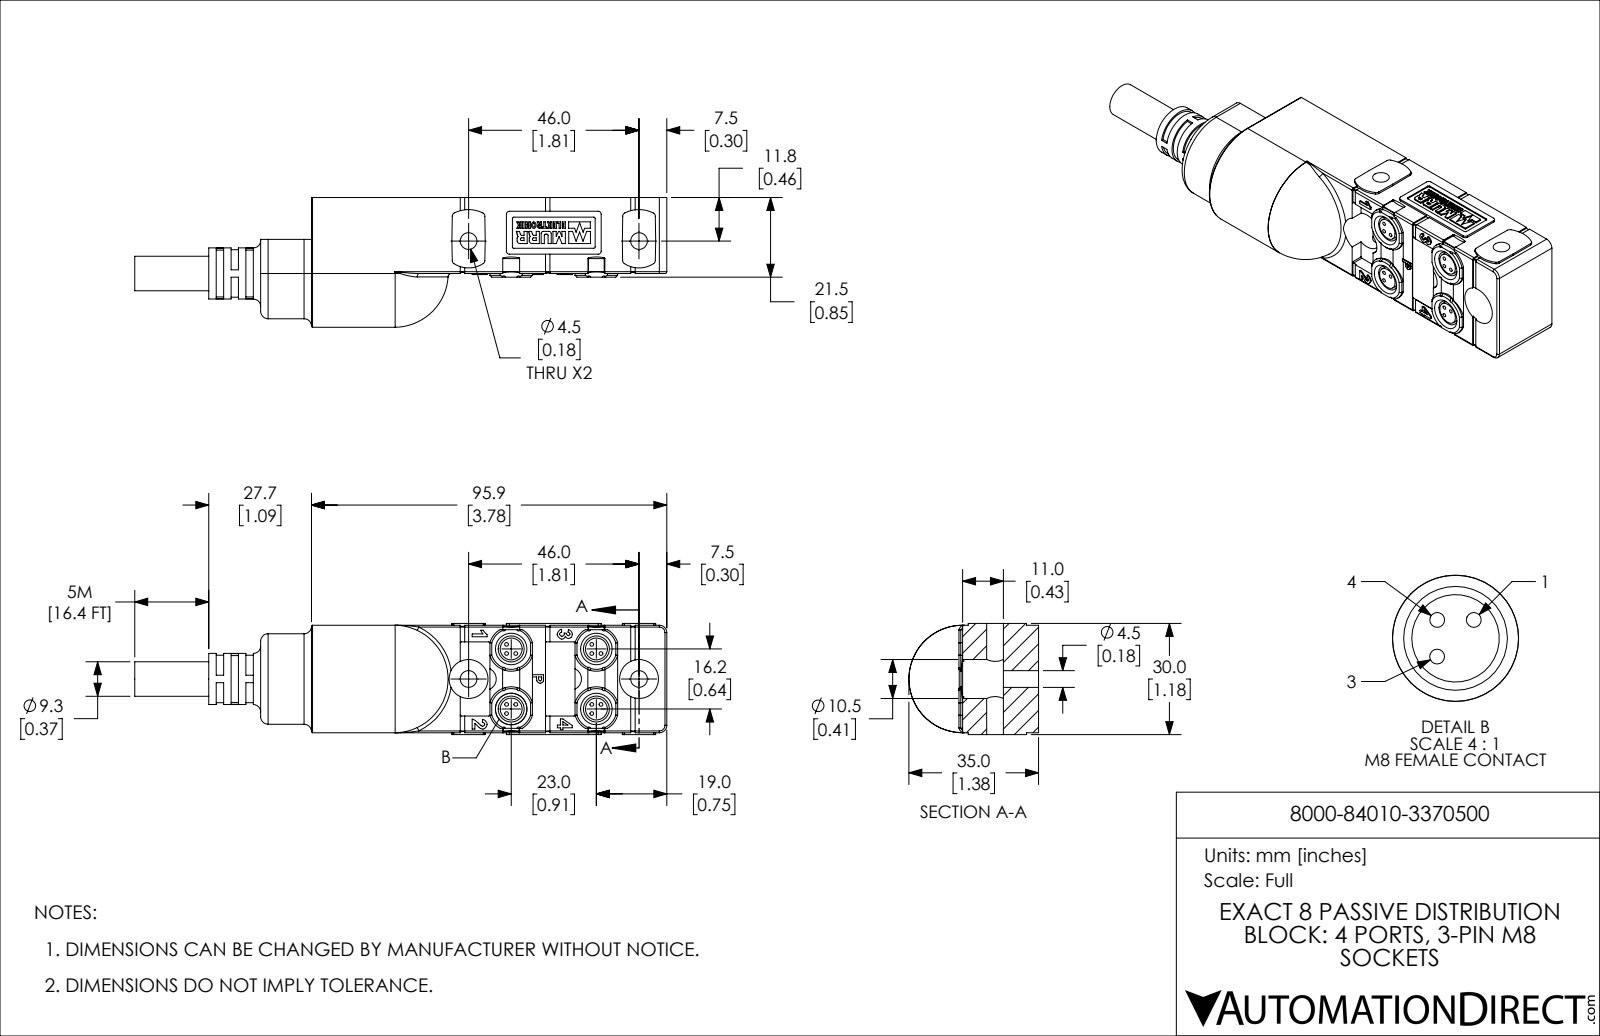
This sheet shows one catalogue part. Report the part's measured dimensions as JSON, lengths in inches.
{"part_name": "8000-84010-3370500", "step_written_by": "SolidWorks 2019 (CONFIG_CONTROL_DESIGN)", "units": "inches", "bodies": {"solids": 1, "faces": 971, "planar": 581, "cylindrical": 285, "other": 105}, "overall_size": [5.654, 1.378, 1.181], "volume_in3": 4.519, "surface_area_in2": 25.67, "round_holes": [[0.039, 12], [0.177, 4], [0.276, 4], [0.413, 2]], "round_bosses_or_shafts": [[0.232, 4], [0.543, 1], [0.504, 1], [0.449, 1], [0.366, 1]], "partial_cylinders_radius": [[0.02, 19], [0.008, 12], [0.012, 10], [0.039, 8], [0.079, 6], [0.394, 6], [0.012, 4], [0.012, 4]], "face_to_face_distances": [1.142, 0.02, 1.161, 0.807, 0.795, 0.433, 0.362, 0.445, 1.181, 3.776], "hole_center_spacings": [0.069, 0.591, 0.098, 0.638, 0.906, 0.956, 0.138, 0.486]}
